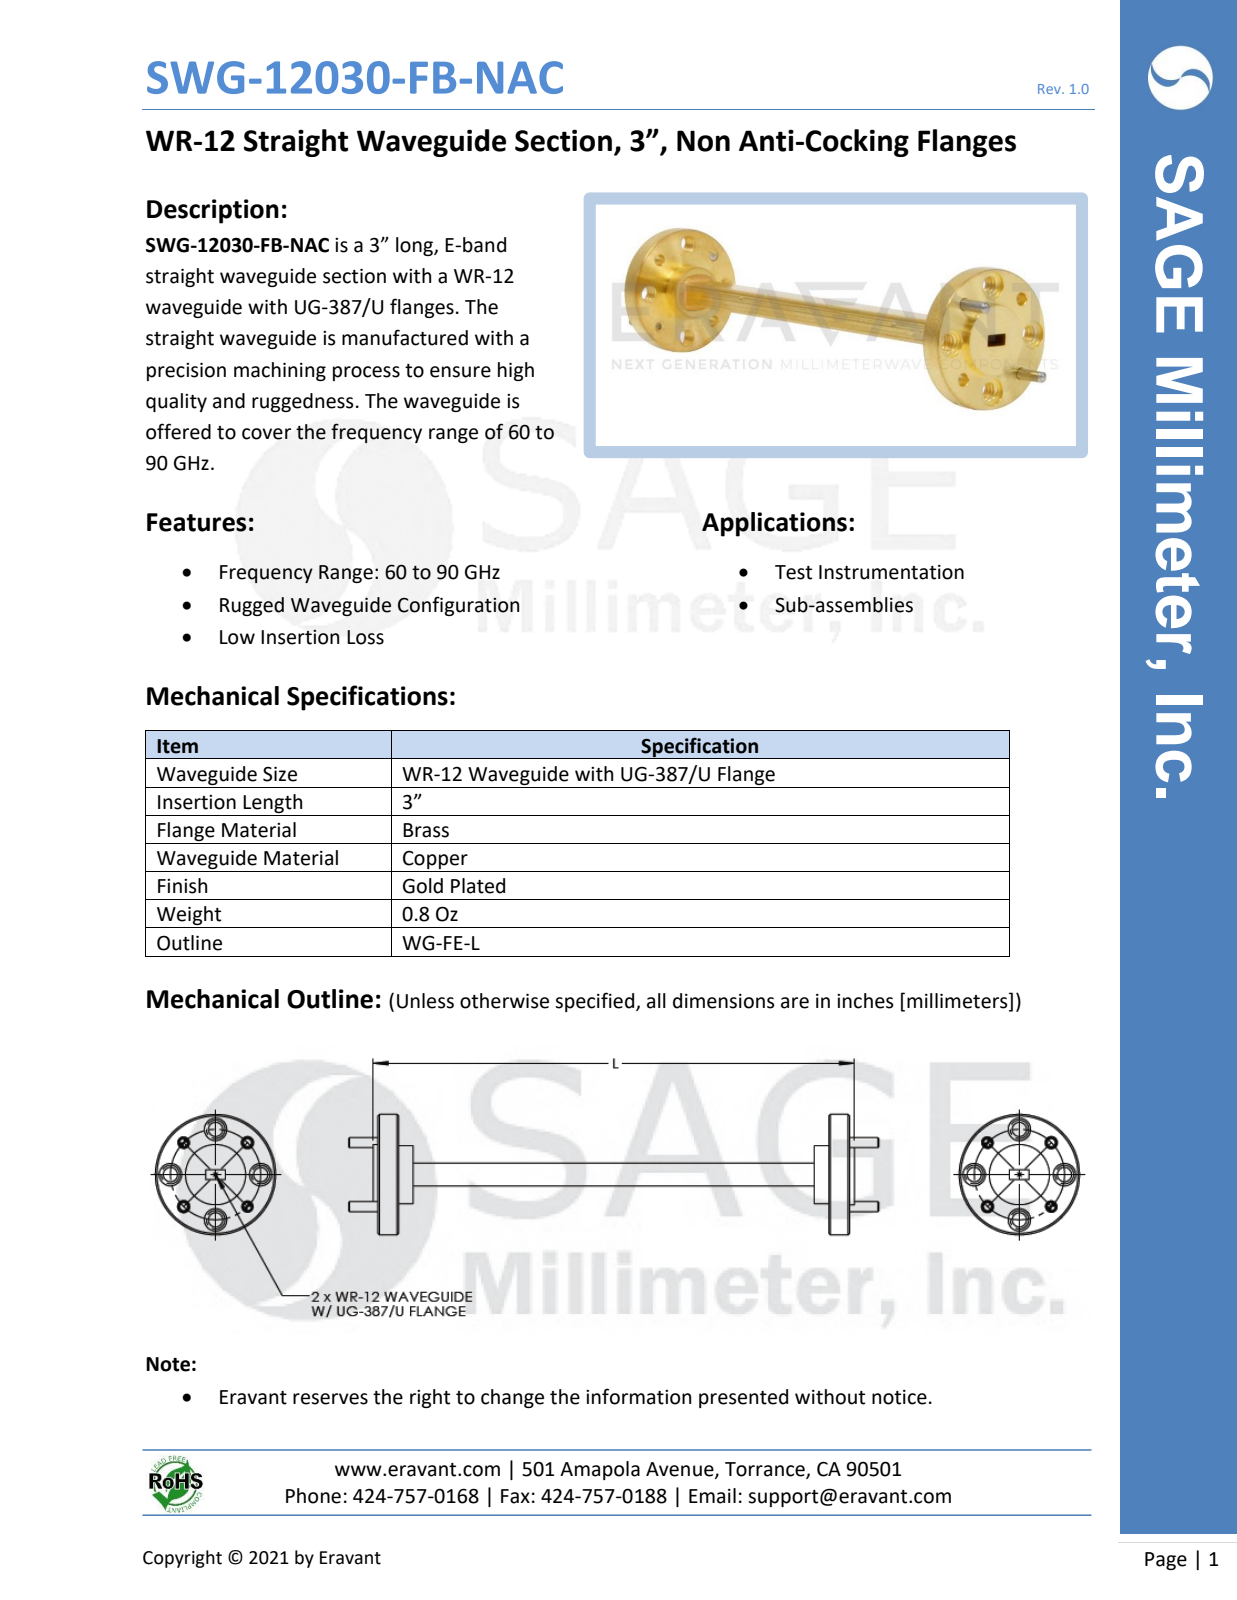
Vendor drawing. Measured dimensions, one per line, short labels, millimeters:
name: SWG-12030-FB
written by: SolidWorks 2016 (AUTOMOTIVE_DESIGN)
unit: mm
bodies: 5 solids, 146 faces (38 planar, 68 cylindrical, 40 other)
size: 83.9 × 19.1 × 19.1
volume: 3 330 mm³; area: 3 155 mm²
holes: 4× ⌀1.5, 4× ⌀1.7, 4× ⌀2.3, 4× ⌀3.6
bosses: 4× ⌀1.6, 1× ⌀19.1, 1× ⌀9.5, 1× ⌀9.1
face distances: 3.6, 3.3, 71.4, 5.1, 68.1, 74.7, 6.4, 69.9, 0.8, 4.1
hole spacings: 5.5, 10.1, 13.2, 14.3, 13.2, 14.3
